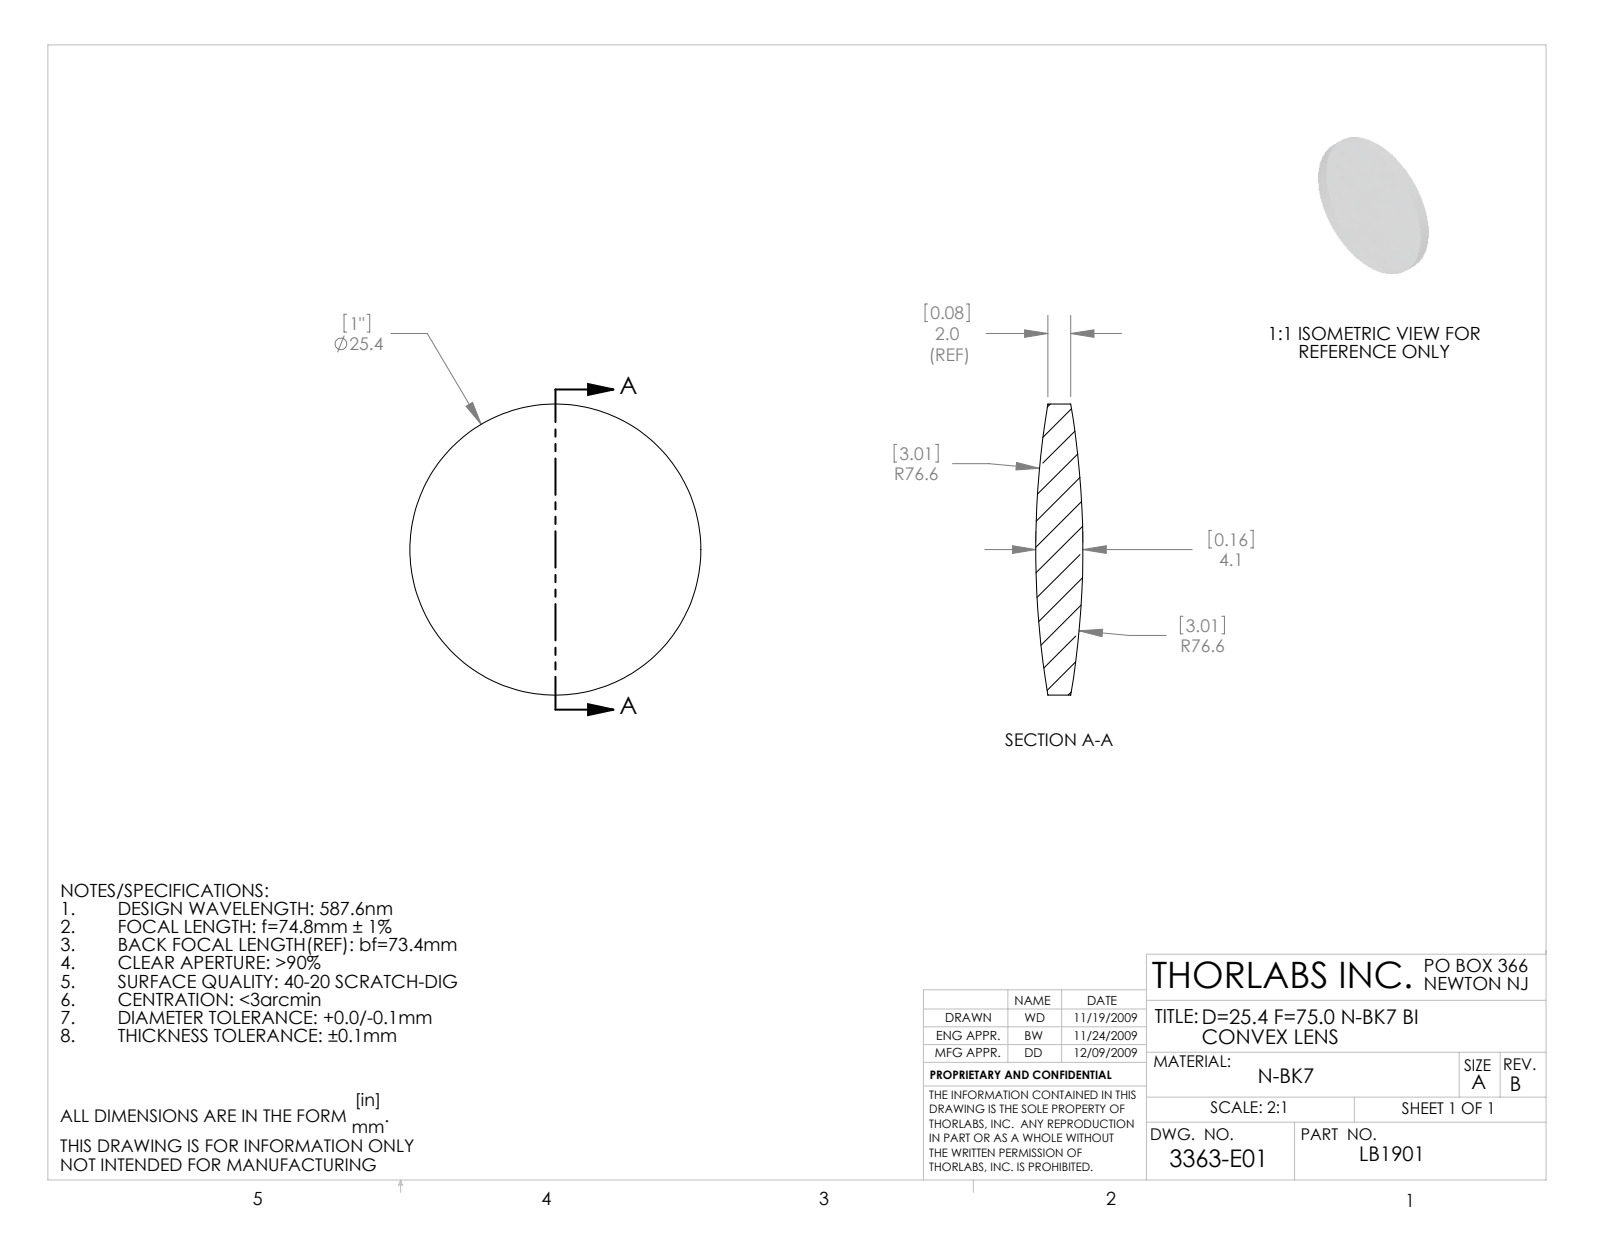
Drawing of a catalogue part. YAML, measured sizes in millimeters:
part_name: "3363-E0W"
step_written_by: "SolidWorks 2009 (AUTOMOTIVE_DESIGN)"
units: millimeters
bodies: {solids: 1, faces: 6, planar: 0, cylindrical: 2, other: 4}
overall_size: [25.4, 25.4, 4.12]
volume: 1551
surface_area: 1180
round_bosses_or_shafts:
  - {diameter: 25.4, count: 1}
